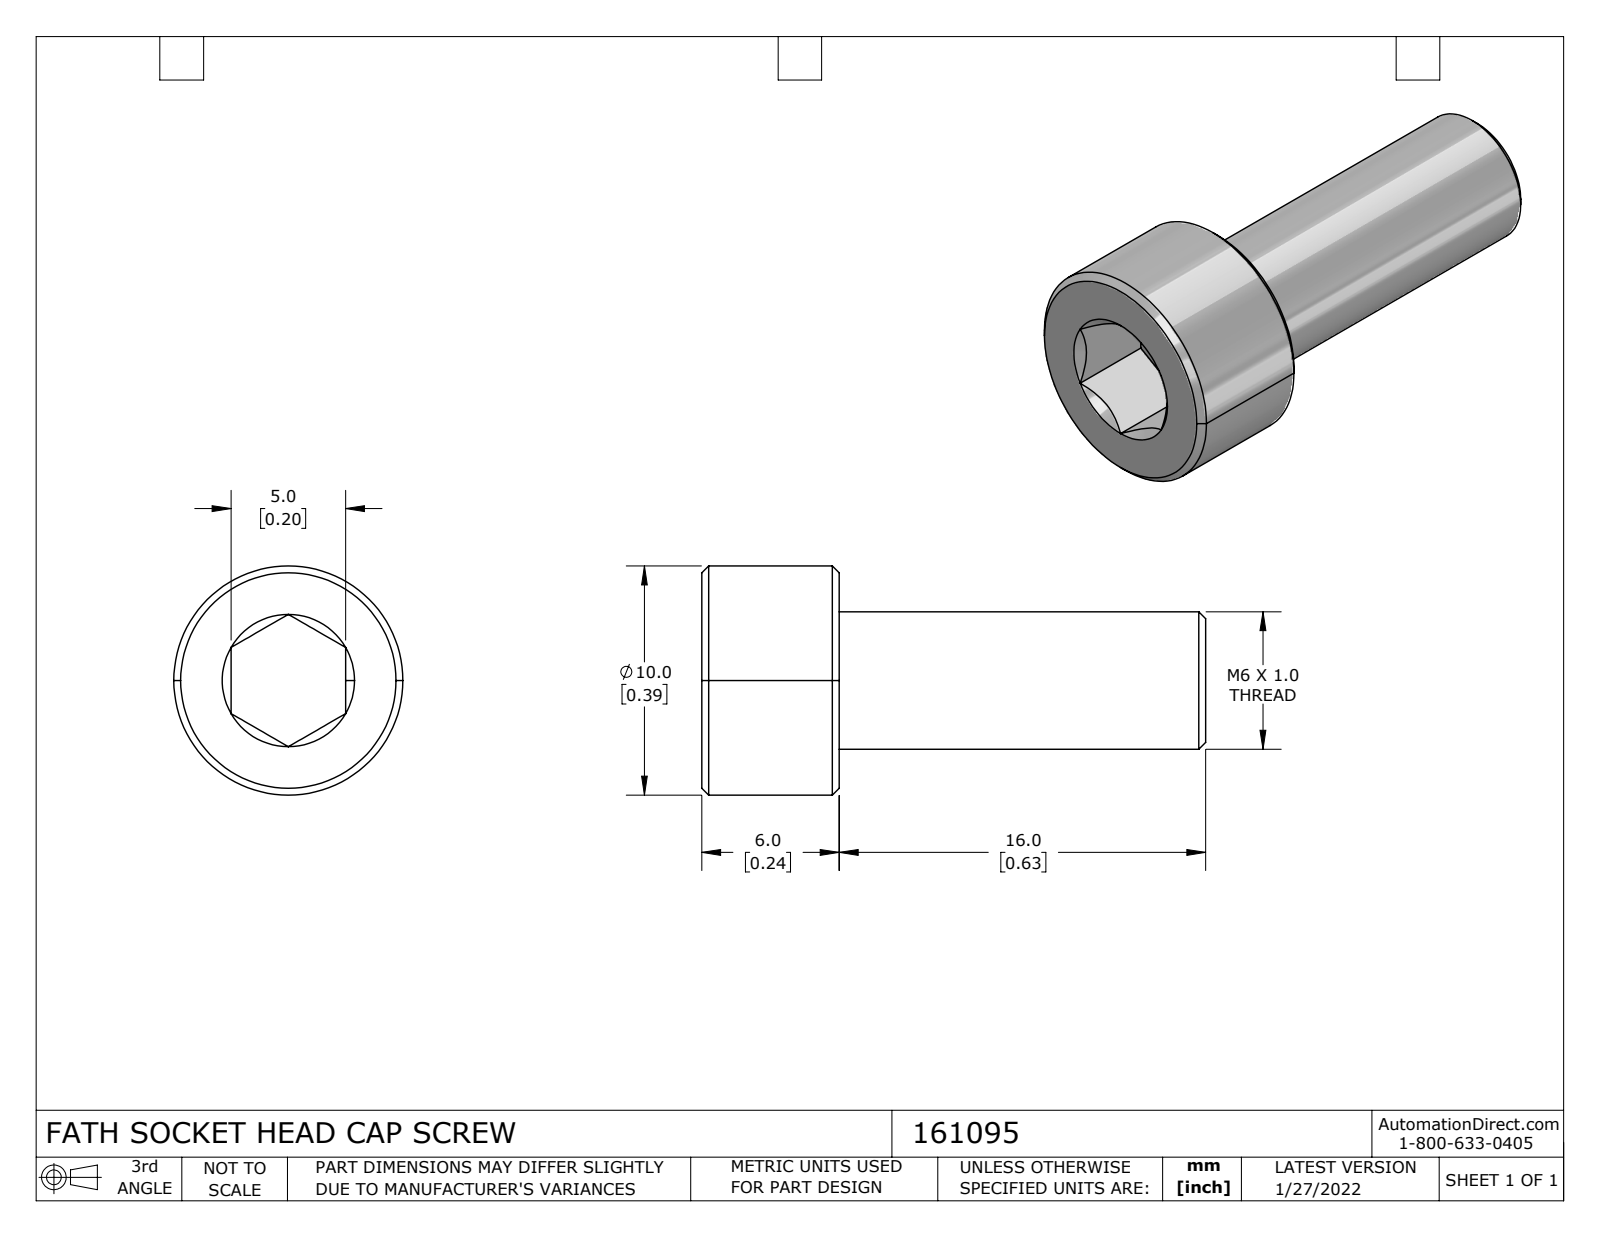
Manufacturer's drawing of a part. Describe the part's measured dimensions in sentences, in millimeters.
The part is named "161095". Its 3-D file was written by "SolidWorks 2021 (CONFIG_CONTROL_DESIGN)". It is 1 solid with 27 faces: 10 planar, 4 cylindrical and 13 other. Overall it measures 22 by 10 by 10 millimeters. Its volume is 838 cubic millimeters and its surface area 695 square millimeters. Round bosses or shafts: 1 of diameter 10, 1 of diameter 6. The main face-to-face distances are 6, 5, 22, 16, 3.75, 2.25, 18.25.
